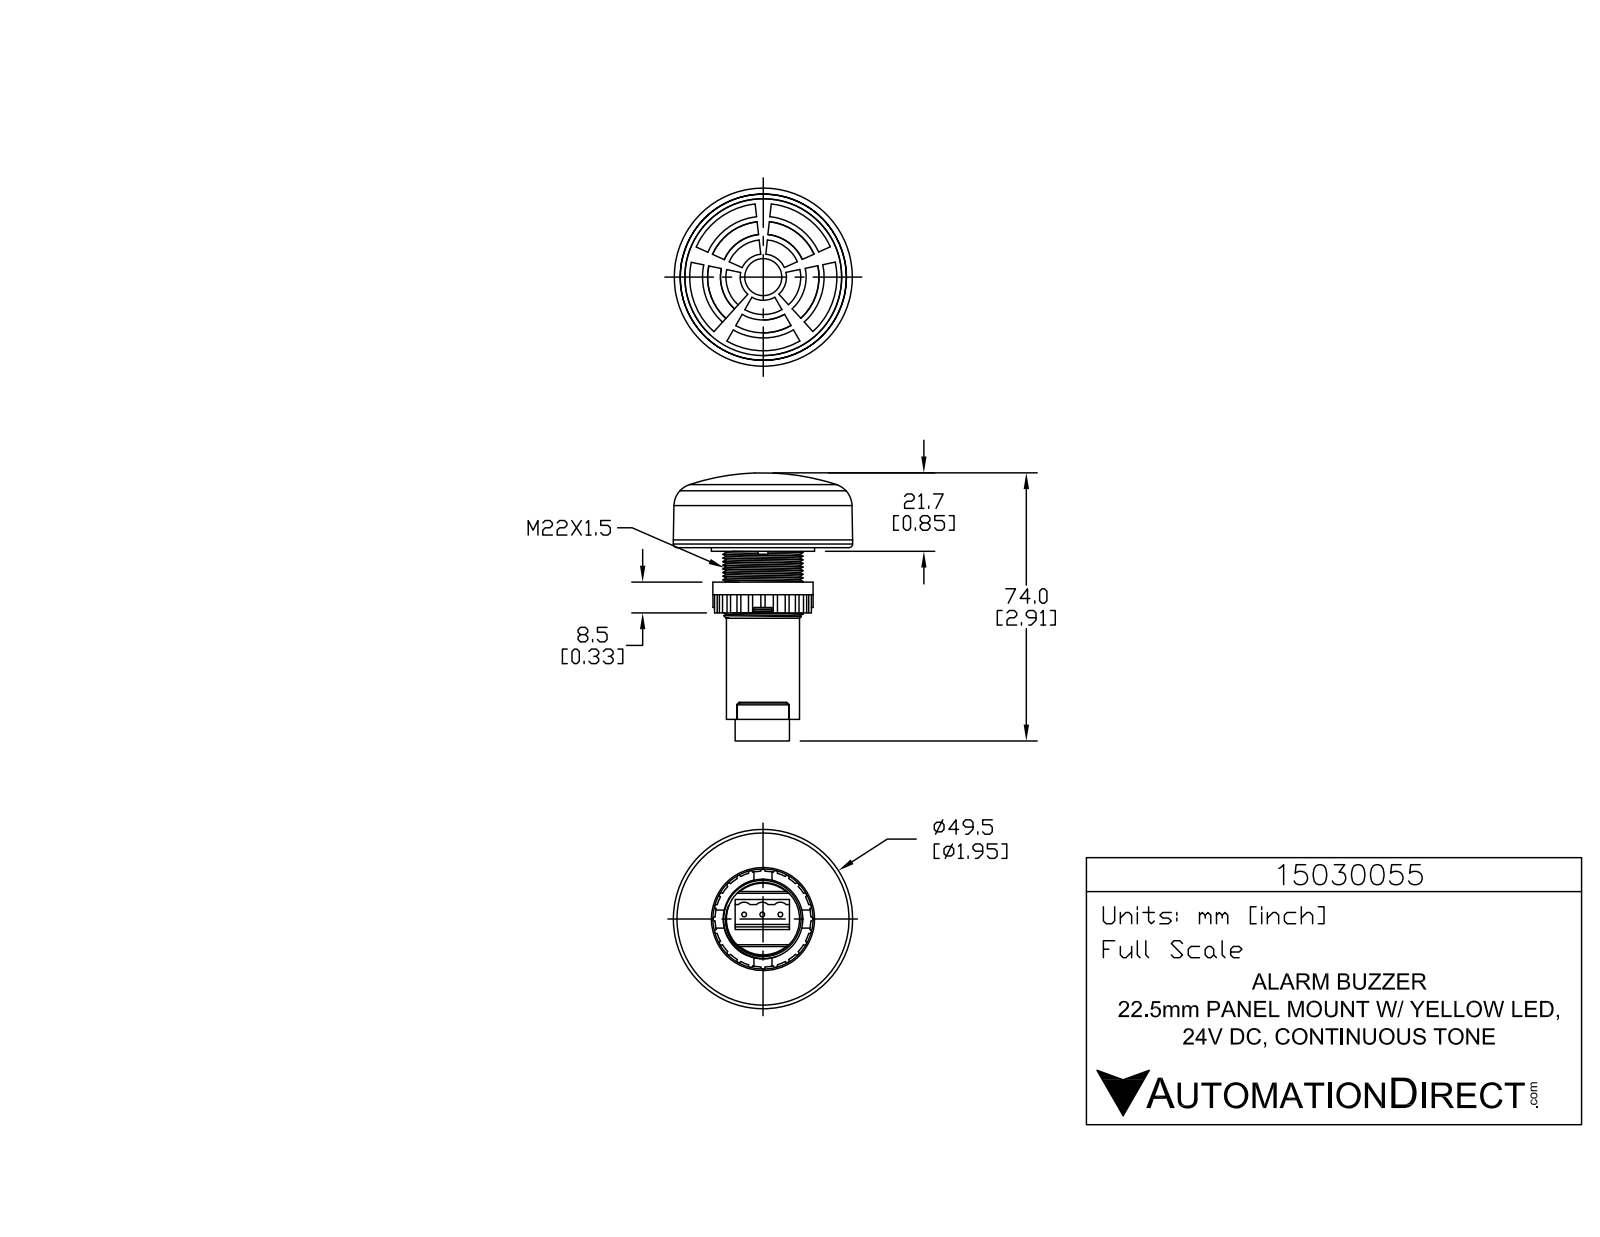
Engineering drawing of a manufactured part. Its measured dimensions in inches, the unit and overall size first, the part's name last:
Units: inches
Overall size (bounding box): 2.823 × 1.956 × 1.952
Round holes (diameter × count): ⌀0.039 ×4
Round bosses / shafts (diameter × count): ⌀0.226 ×4, ⌀0.056 ×4, ⌀0.051 ×3, ⌀1.949 ×1, ⌀1.807 ×1, ⌀1.122 ×1, ⌀1.091 ×1, ⌀0.866 ×1
Partial cylindrical surfaces — rounded edges, fillets, slot ends (radius × count): R0.023 ×24, R0.008 ×8, R0.008 ×8, R0.008 ×8, R0.131 ×8, R0.004 ×4, R0.005 ×4, R0.008 ×4
Main face-to-face distances: 0.335, 0.374, 0.039, 1.398, 1.732, 1.772, 0.709, 1.063, 0.669, 1.297
Volume: 3.113 in³ · Surface area: 19.88 in²
Bodies: 1 solid, 1200 faces (744 planar, 322 cylindrical, 134 other)
Part name (STEP PRODUCT): 15030055
STEP written by: SolidWorks 2017 (AUTOMOTIVE_DESIGN)
